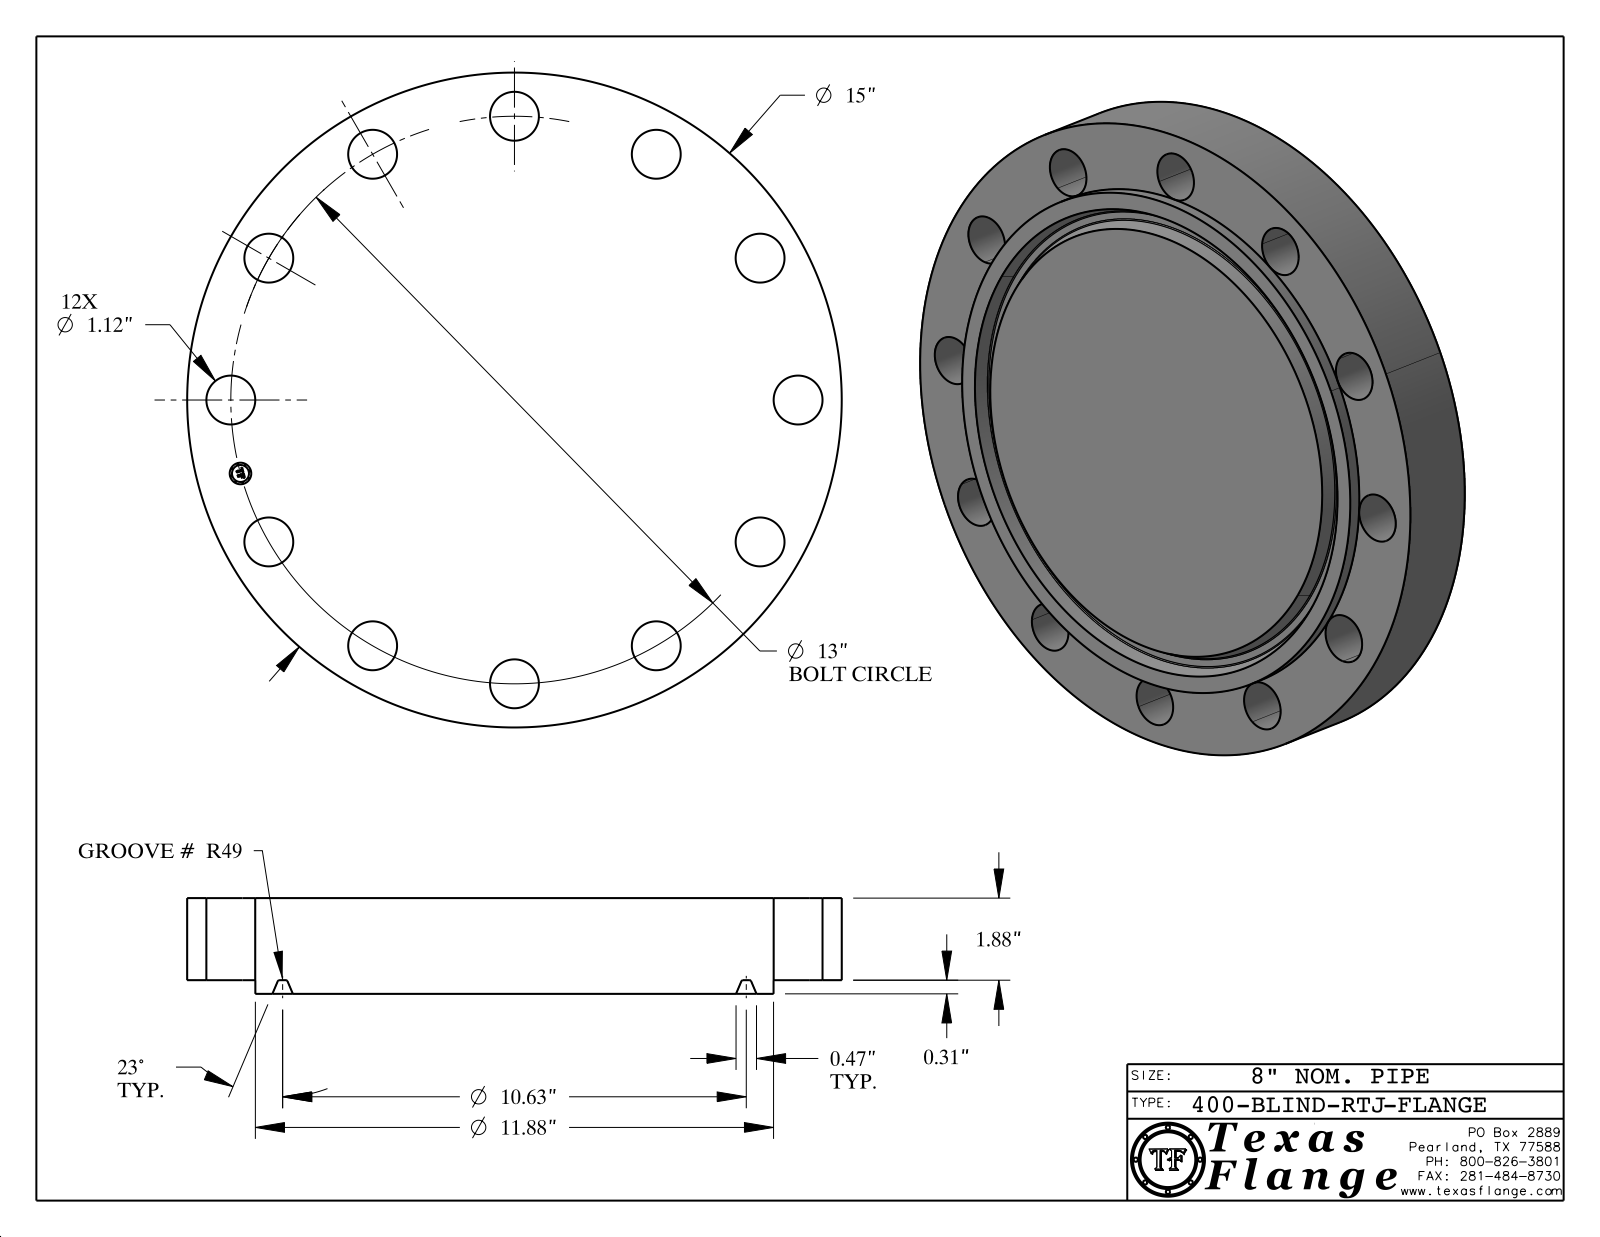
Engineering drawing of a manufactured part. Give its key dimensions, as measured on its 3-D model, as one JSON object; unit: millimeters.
{"part_name": "400-BLIND-RTJ", "step_written_by": "CATIA V5 STEP AP214 (AUTOMOTIVE_DESIGN)", "units": "millimeters", "bodies": {"solids": 1, "faces": 426, "planar": 370, "cylindrical": 48, "other": 8}, "overall_size": [381, 381, 55.7], "volume_mm3": 5590000, "surface_area_mm2": 337400, "round_holes": [[28.4, 12], [12.6, 1]], "round_bosses_or_shafts": [[0.8, 8], [381, 1], [301.6, 1], [9.9, 1]], "face_to_face_distances": [55.7, 8, 47.8, 55.3, 47.4, 0.4, 3.8, 3.7, 0.7, 2.4], "hole_center_spacings": [85.5, 165.1, 233.5, 286, 318.9, 330.2, 43.1, 126.4]}
